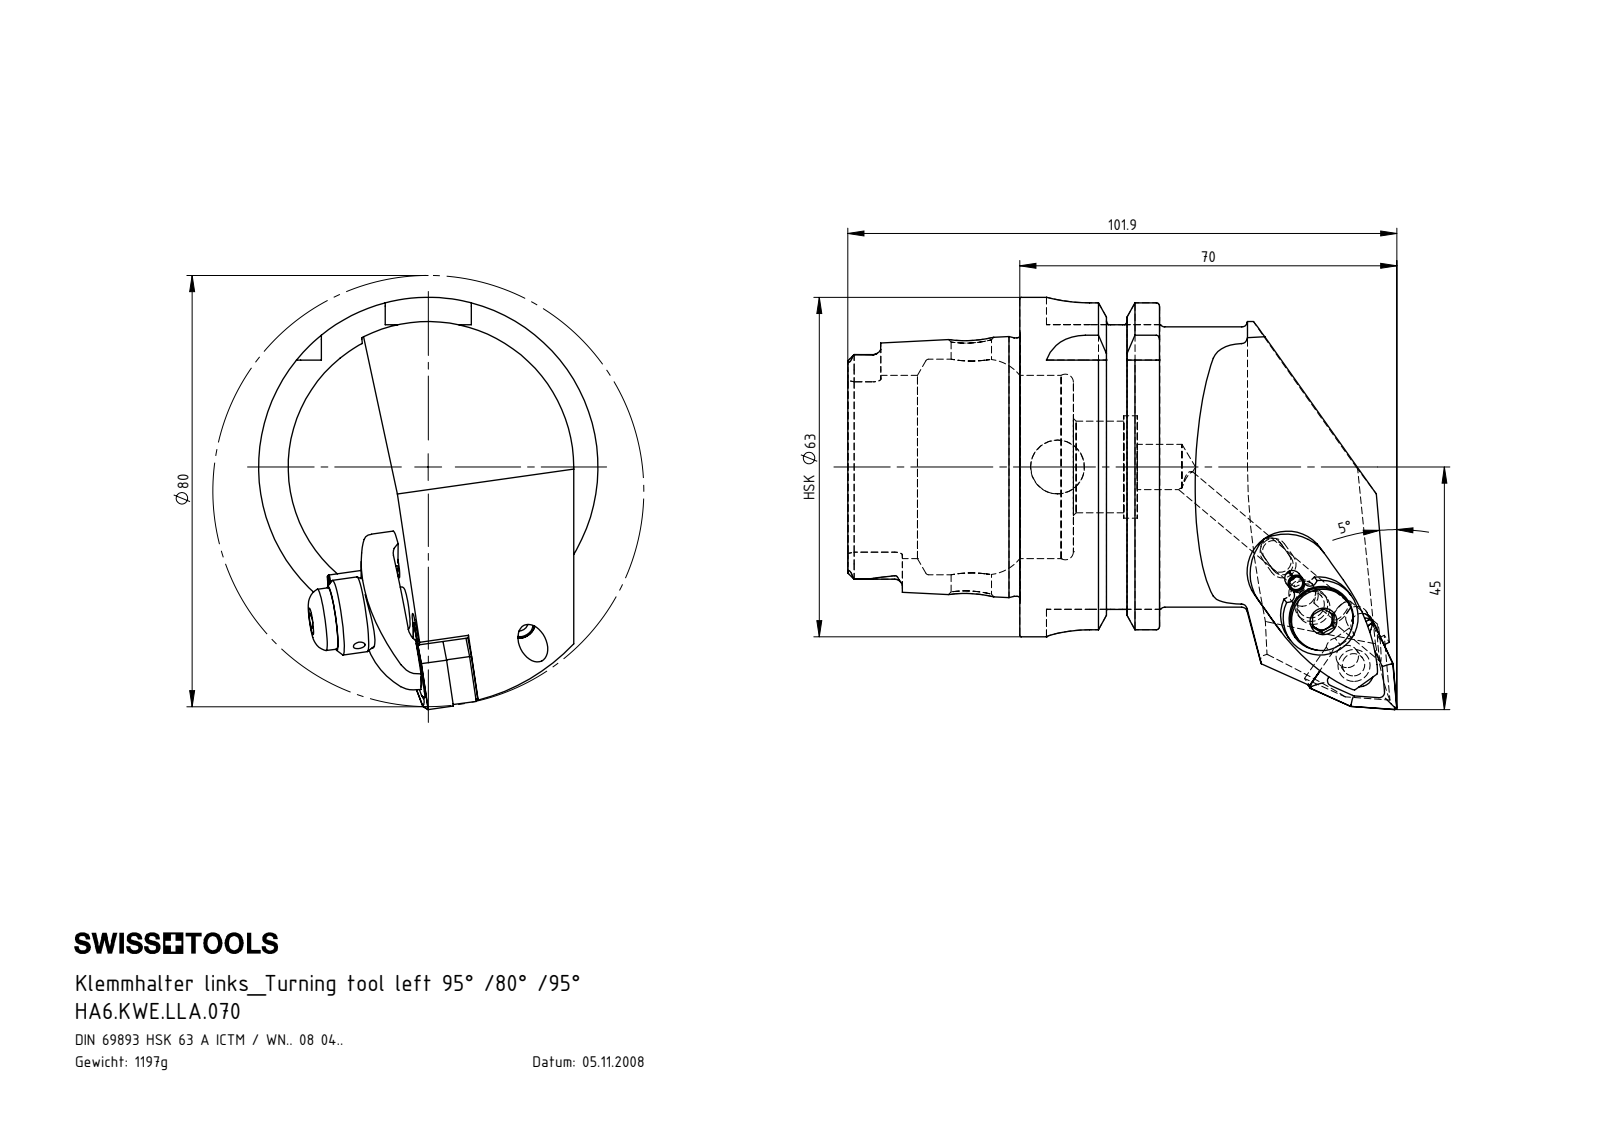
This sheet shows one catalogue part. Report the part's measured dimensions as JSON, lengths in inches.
{"part_name": "WCC-ER5.102.005_A; WCC-ER2.001.010_A; WCC-ER5.102.012_B; WWE-ER2.101.004_A (+7 more)", "step_written_by": "SolidWorks 2017 (AUTOMOTIVE_DESIGN)", "units": "inches", "bodies": {"solids": 11, "faces": 482, "planar": 135, "cylindrical": 153, "other": 194}, "overall_size": [4.012, 3.012, 2.48], "volume_in3": 9.275, "surface_area_in2": 54.96, "round_holes": [[0.079, 3], [0.165, 2], [0.197, 2], [0.276, 2], [0.094, 1], [0.118, 1], [0.157, 1], [0.203, 1], [0.244, 1], [0.264, 1], [0.295, 1], [0.307, 1]], "round_bosses_or_shafts": [[0.197, 2], [0.118, 2], [2.48, 1], [2.163, 1], [2.047, 1], [1.887, 1], [0.551, 1], [0.453, 1]], "partial_cylinders_radius": [[0.015, 6], [0.027, 6], [0.055, 6], [0.016, 4], [0.315, 4], [0.059, 3], [0.079, 3], [0.111, 2]], "face_to_face_distances": [1.022, 0.63, 0.392, 1.256, 1.648, 2.278, 0.187, 2.079, 0.858, 0.177], "hole_center_spacings": [0.315, 0.585, 0.587, 0.9, 0.902, 0.323, 0.323, 0.577]}
